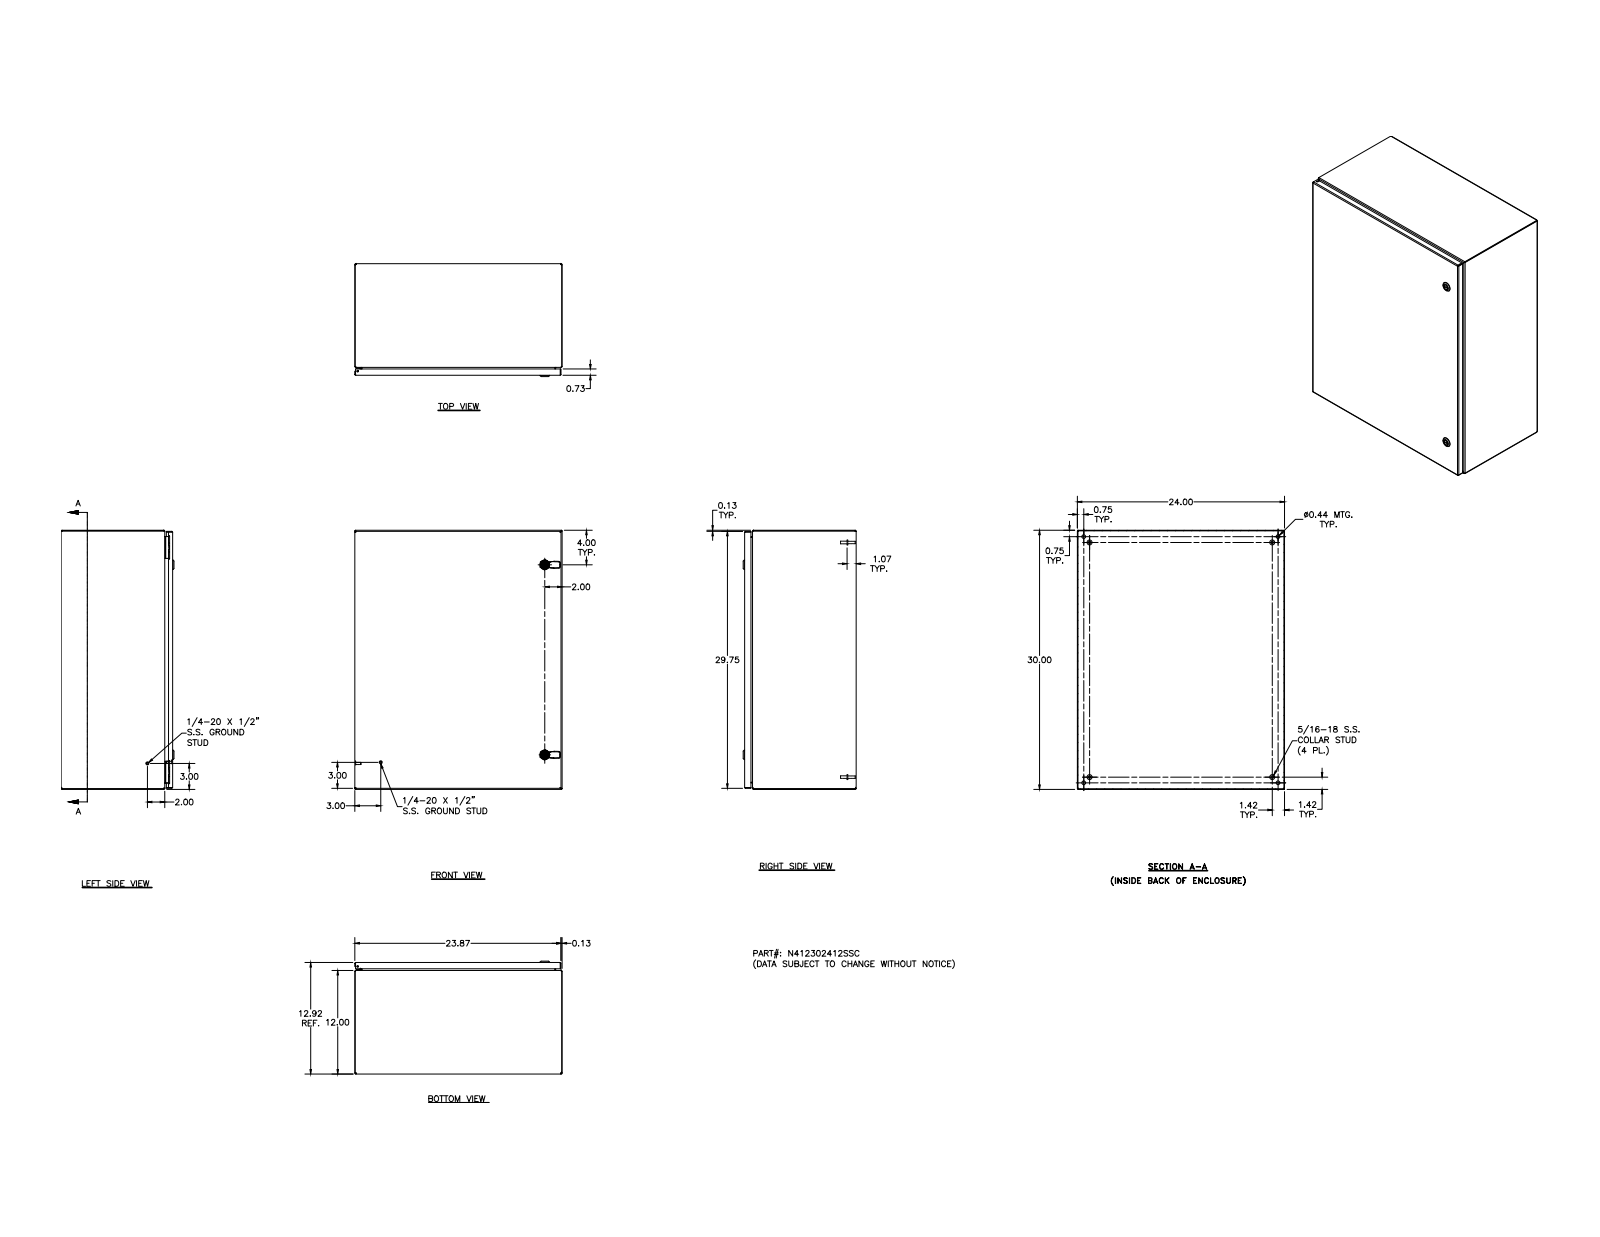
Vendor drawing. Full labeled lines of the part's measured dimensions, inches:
Part name (STEP PRODUCT): N412302412SSC; N412302412SSCBKP; 388151; N4123024SSCLID (+8 more)
STEP written by: Autodesk Inventor 2011 (AUTOMOTIVE_DESIGN)
Units: inches
Bodies: 42 solids, 1682 faces (706 planar, 600 cylindrical, 376 other)
Overall size (bounding box): 30 × 24 × 13.075
Volume: 218.8 in³ · Surface area: 5 934 in²
Round holes (diameter × count): ⌀0.188 ×5, ⌀0.093 ×4, ⌀0.152 ×4, ⌀0.167 ×4, ⌀0.172 ×4, ⌀0.437 ×4, ⌀0.156 ×2, ⌀0.197 ×2, ⌀0.315 ×2, ⌀0.394 ×2, ⌀0.402 ×2, ⌀0.634 ×2
Round bosses / shafts (diameter × count): ⌀0.25 ×10, ⌀0.563 ×4, ⌀0.36 ×4, ⌀0.32 ×4, ⌀0.3 ×4, ⌀0.275 ×4, ⌀0.256 ×4, ⌀0.164 ×4
Partial cylindrical surfaces — rounded edges, fillets, slot ends (radius × count): R0.031 ×30, R0.05 ×26, R0.105 ×20, R0.016 ×18, R0.02 ×15, R0.125 ×14, R0.032 ×8, R0.07 ×8
Main face-to-face distances: 0.074, 12.843, 23.926, 12.917, 12.769, 29.926, 23.852, 24, 30, 29.852
Hole centre spacings: 26, 0.017, 0.66, 22.869, 0.019, 0.5, 0.648, 0.652
